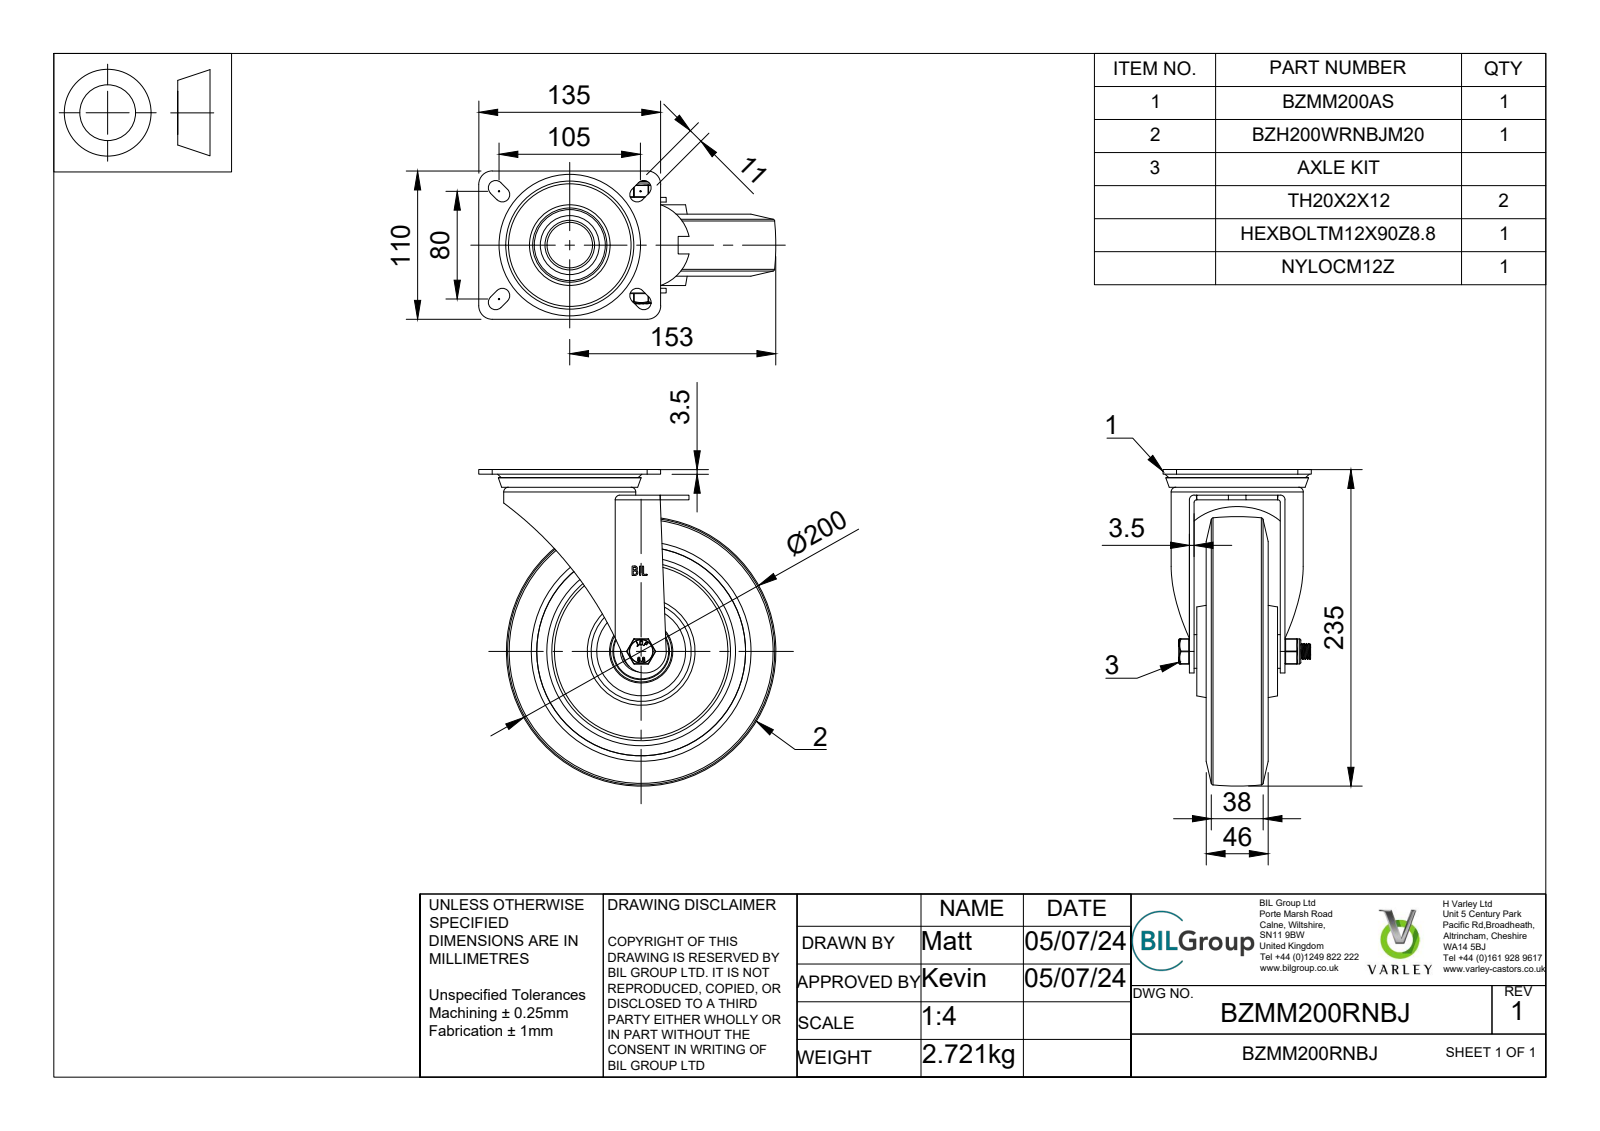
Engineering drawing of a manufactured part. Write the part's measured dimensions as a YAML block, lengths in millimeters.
part_name: "BZMM200RNBJ v3; BZMM200AS - 2 - 64 v1; ZINC PLATED, PRESSED STEEL TOP PLATE; ZINC PLATED, PRESSED STEEL TOP PLATE Geometry (+7 more)"
step_written_by: "Autodesk Translation Framework v13.14.0.145 (AUTOMOTIVE_DESIGN)"
units: millimeters
bodies: {solids: 77, faces: 1155, planar: 464, cylindrical: 206, other: 485}
overall_size: [235, 220.5, 110]
volume: 1170000
surface_area: 314407
round_holes:
  - {diameter: 12, count: 1}
  - {diameter: 12.2, count: 1}
  - {diameter: 14, count: 1}
  - {diameter: 20, count: 1}
  - {diameter: 28.5, count: 1}
  - {diameter: 30.8, count: 1}
  - {diameter: 33.75, count: 1}
  - {diameter: 40.3, count: 1}
  - {diameter: 40.5, count: 1}
  - {diameter: 42, count: 1}
  - {diameter: 45.5, count: 1}
  - {diameter: 47, count: 1}
round_bosses_or_shafts:
  - {diameter: 98, count: 1}
  - {diameter: 78, count: 1}
  - {diameter: 50, count: 1}
  - {diameter: 40.8, count: 1}
  - {diameter: 39.75, count: 1}
  - {diameter: 31.3, count: 1}
  - {diameter: 27, count: 1}
  - {diameter: 25, count: 1}
partial_cylinders:
  - {radius: 0.5, count: 19}
  - {radius: 5.5, count: 8}
  - {radius: 0.47, count: 4}
  - {radius: 0.9, count: 4}
  - {radius: 1.75, count: 4}
  - {radius: 10, count: 4}
  - {radius: 0.89, count: 2}
  - {radius: 0.89, count: 2}
face_to_face_distances: [3.5, 9, 19, 12.5, 27, 39.5, 5.5, 28, 36, 55]
